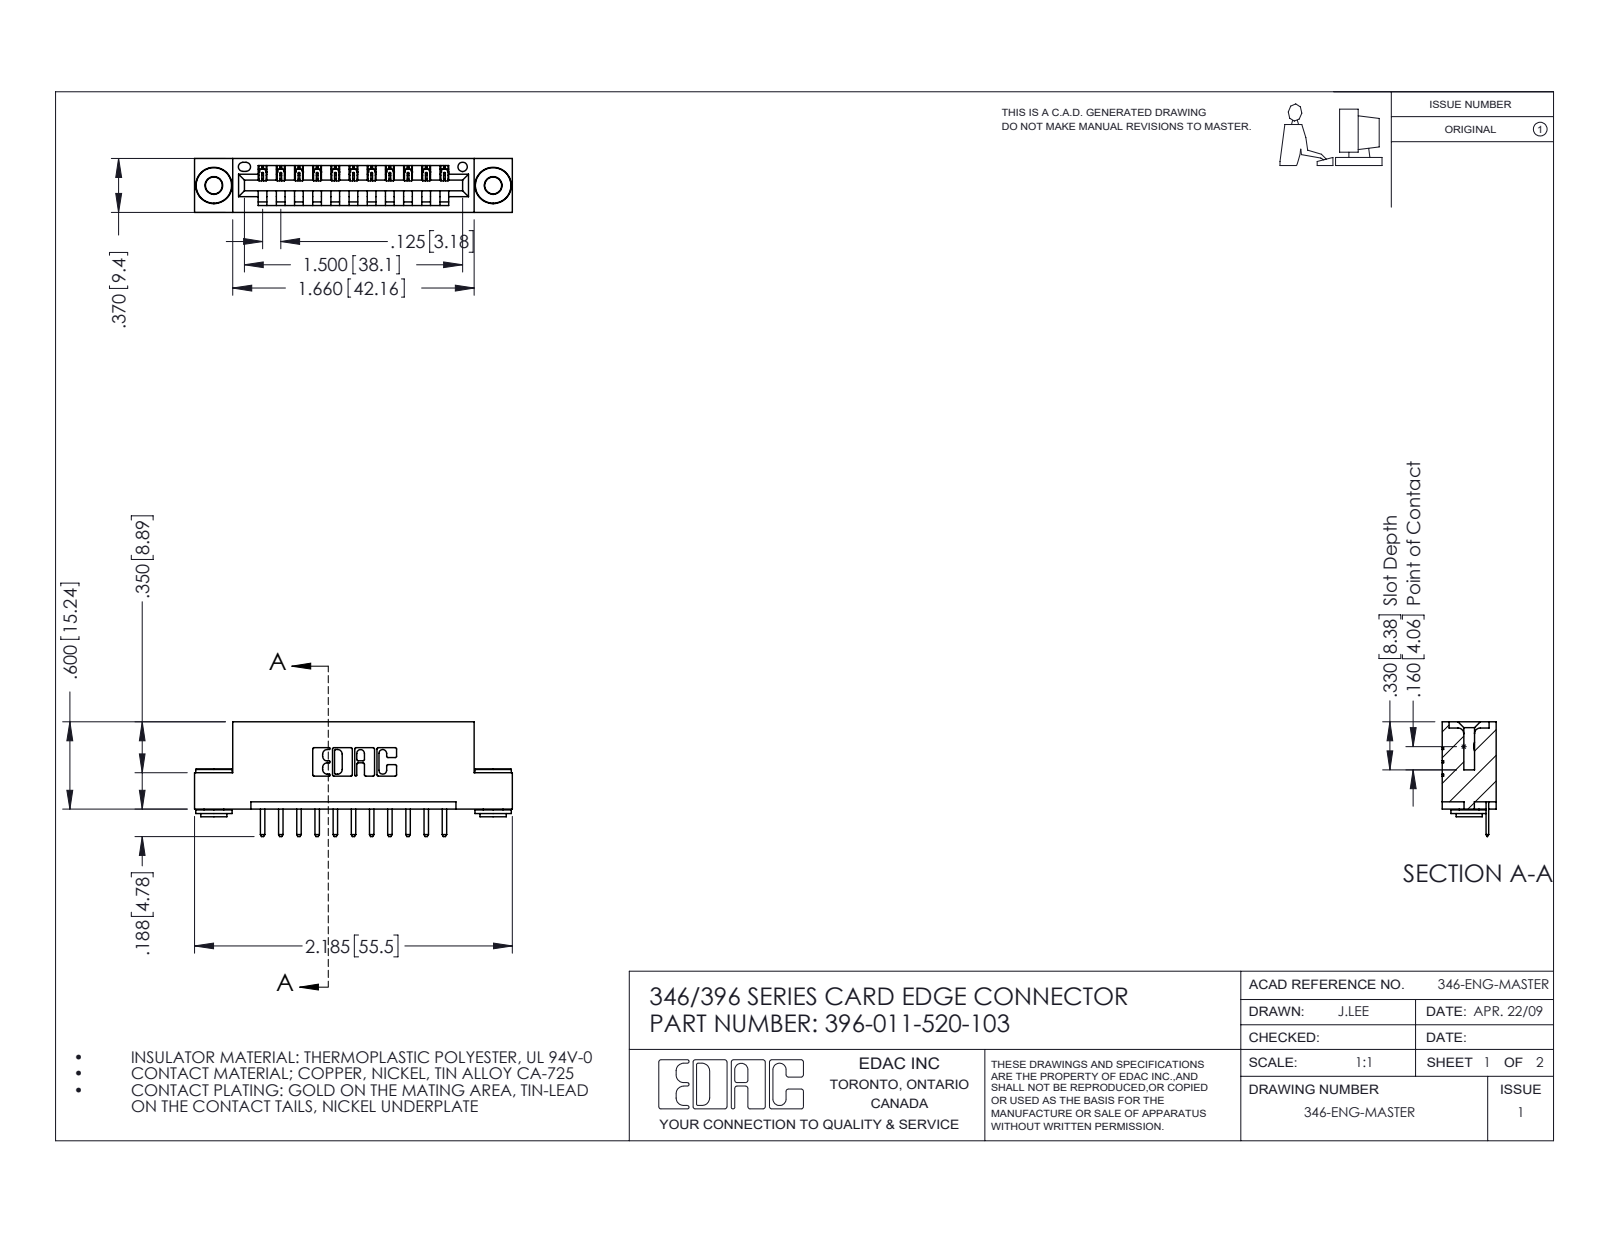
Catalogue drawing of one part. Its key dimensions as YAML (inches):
part_name: "346 Part_Flush Mounting Lugs - 0.156 Dia-TH; 345-292-001_345-293-120; 396-011-520-103; 345-250-002_345-250-002-102"
step_written_by: "SolidWorks 2016 (CONFIG_CONTROL_DESIGN)"
units: inches
bodies: {solids: 14, faces: 842, planar: 548, cylindrical: 286, other: 8}
overall_size: [2.185, 0.788, 0.37]
volume: 0.31
surface_area: 9.512
round_holes:
  - {diameter: 0.116, count: 2}
  - {diameter: 0.156, count: 2}
  - {diameter: 0.064, count: 1}
round_bosses_or_shafts:
  - {diameter: 0.25, count: 2}
  - {diameter: 0.18, count: 2}
  - {diameter: 0.136, count: 2}
partial_cylinders:
  - {radius: 0.01, count: 24}
  - {radius: 0.006, count: 22}
  - {radius: 0.01, count: 22}
  - {radius: 0.007, count: 6}
  - {radius: 0.031, count: 6}
  - {radius: 0.026, count: 3}
  - {radius: 0.031, count: 2}
  - {radius: 0.04, count: 2}
face_to_face_distances: [0.25, 0.37, 0.048, 0.322, 0.148, 0.222, 0.1, 0.174, 0.025, 0.072]
hole_center_spacings: [0.246, 1.715, 1.92]
